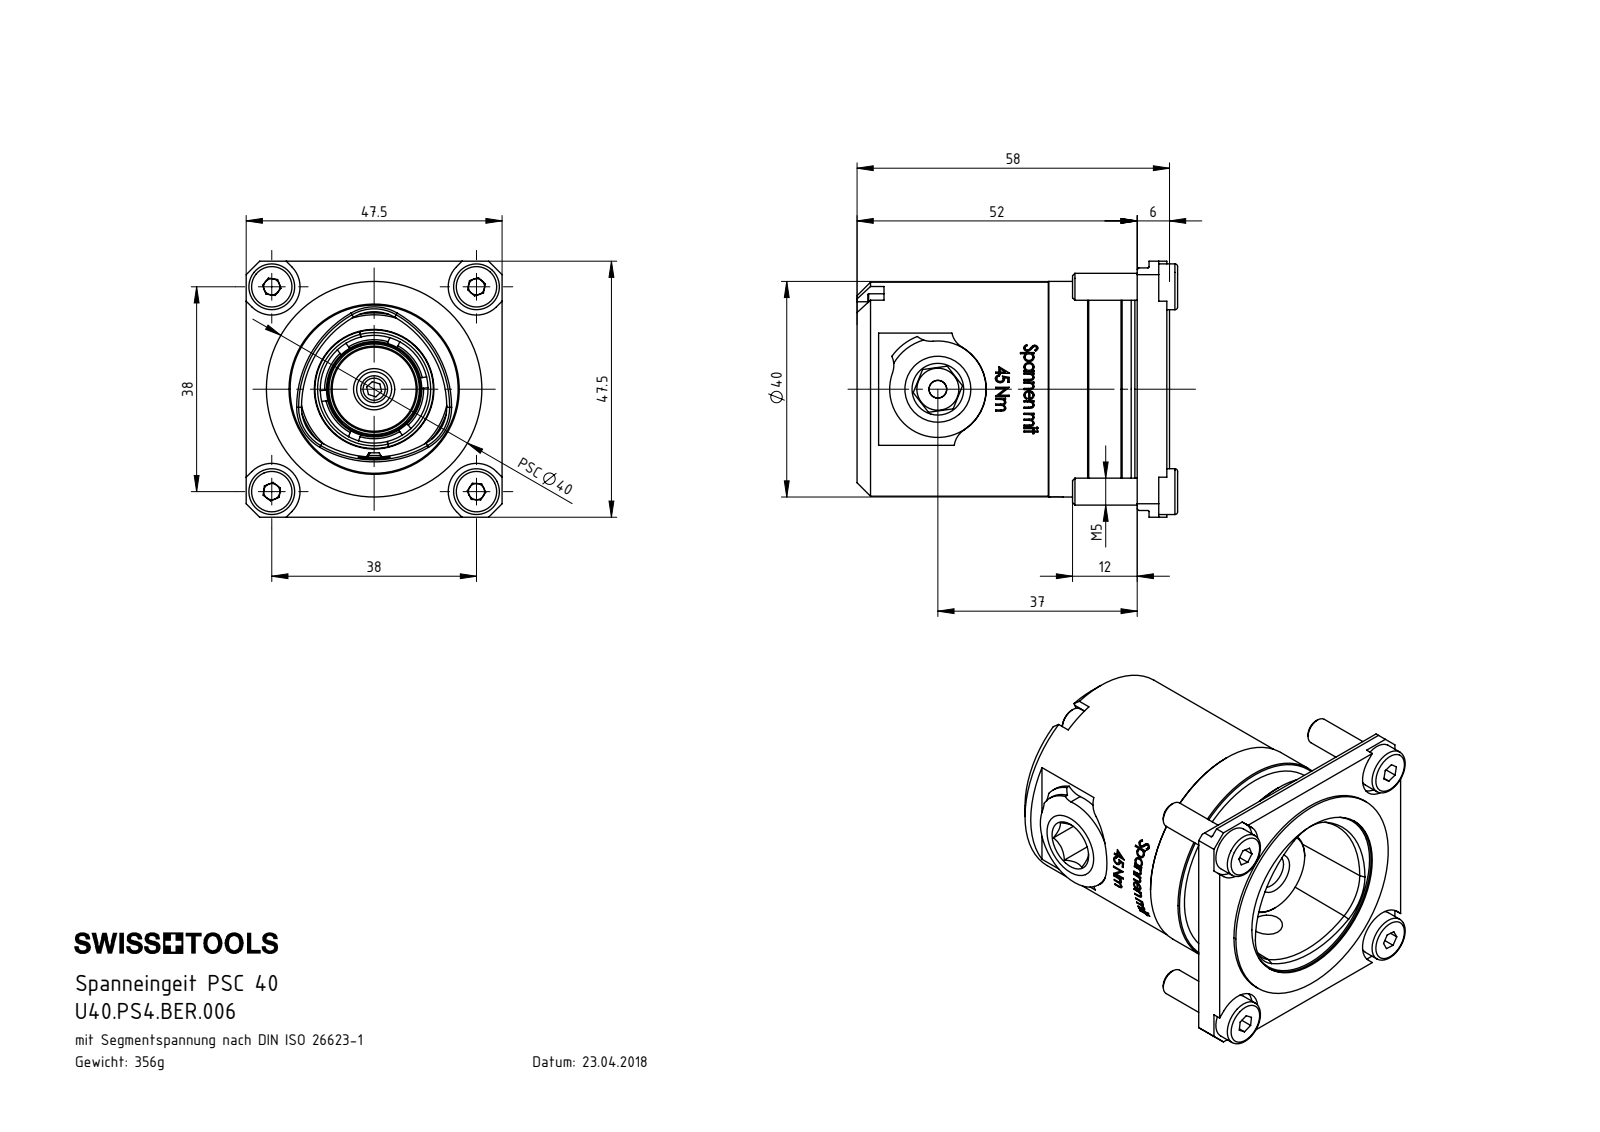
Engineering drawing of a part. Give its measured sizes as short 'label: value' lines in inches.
name: DIN 3771 - 13x1.5; 765.18468.001.0.02; 745.18468.014.0; 777.18468.002.1 (+8 more)
written by: SolidWorks 2017 (AUTOMOTIVE_DESIGN)
unit: in
bodies: 29 solids, 803 faces (300 planar, 180 cylindrical, 323 other)
size: 3.071 × 1.88 × 1.87
volume: 5.573 in³; area: 69.91 in²
holes: 5× ⌀0.098, 4× ⌀0.217, 3× ⌀0.13, 2× ⌀0.083, 1× ⌀0.129, 1× ⌀0.157, 1× ⌀0.165, 1× ⌀0.181, 1× ⌀0.236, 1× ⌀0.256, 1× ⌀0.307, 1× ⌀0.386
bosses: 5× ⌀0.197, 4× ⌀0.335, 2× ⌀0.63, 2× ⌀0.217, 2× ⌀0.118, 1× ⌀1.575, 1× ⌀1.563, 1× ⌀1.457
rounds: 8× R0.012, 8× R0.157, 4× R0.207, 3× R0.118, 2× R0.008, 1× R0.177, 1× R0.27, 1× R0.354
face distances: 1.795, 0.807, 0.866, 1.008, 0.787, 0.236, 0.988, 0.02, 0.65, 0.886
hole spacings: 1.058, 1.496, 0.374, 0.5, 0.649, 1.035, 1.418, 1.683
